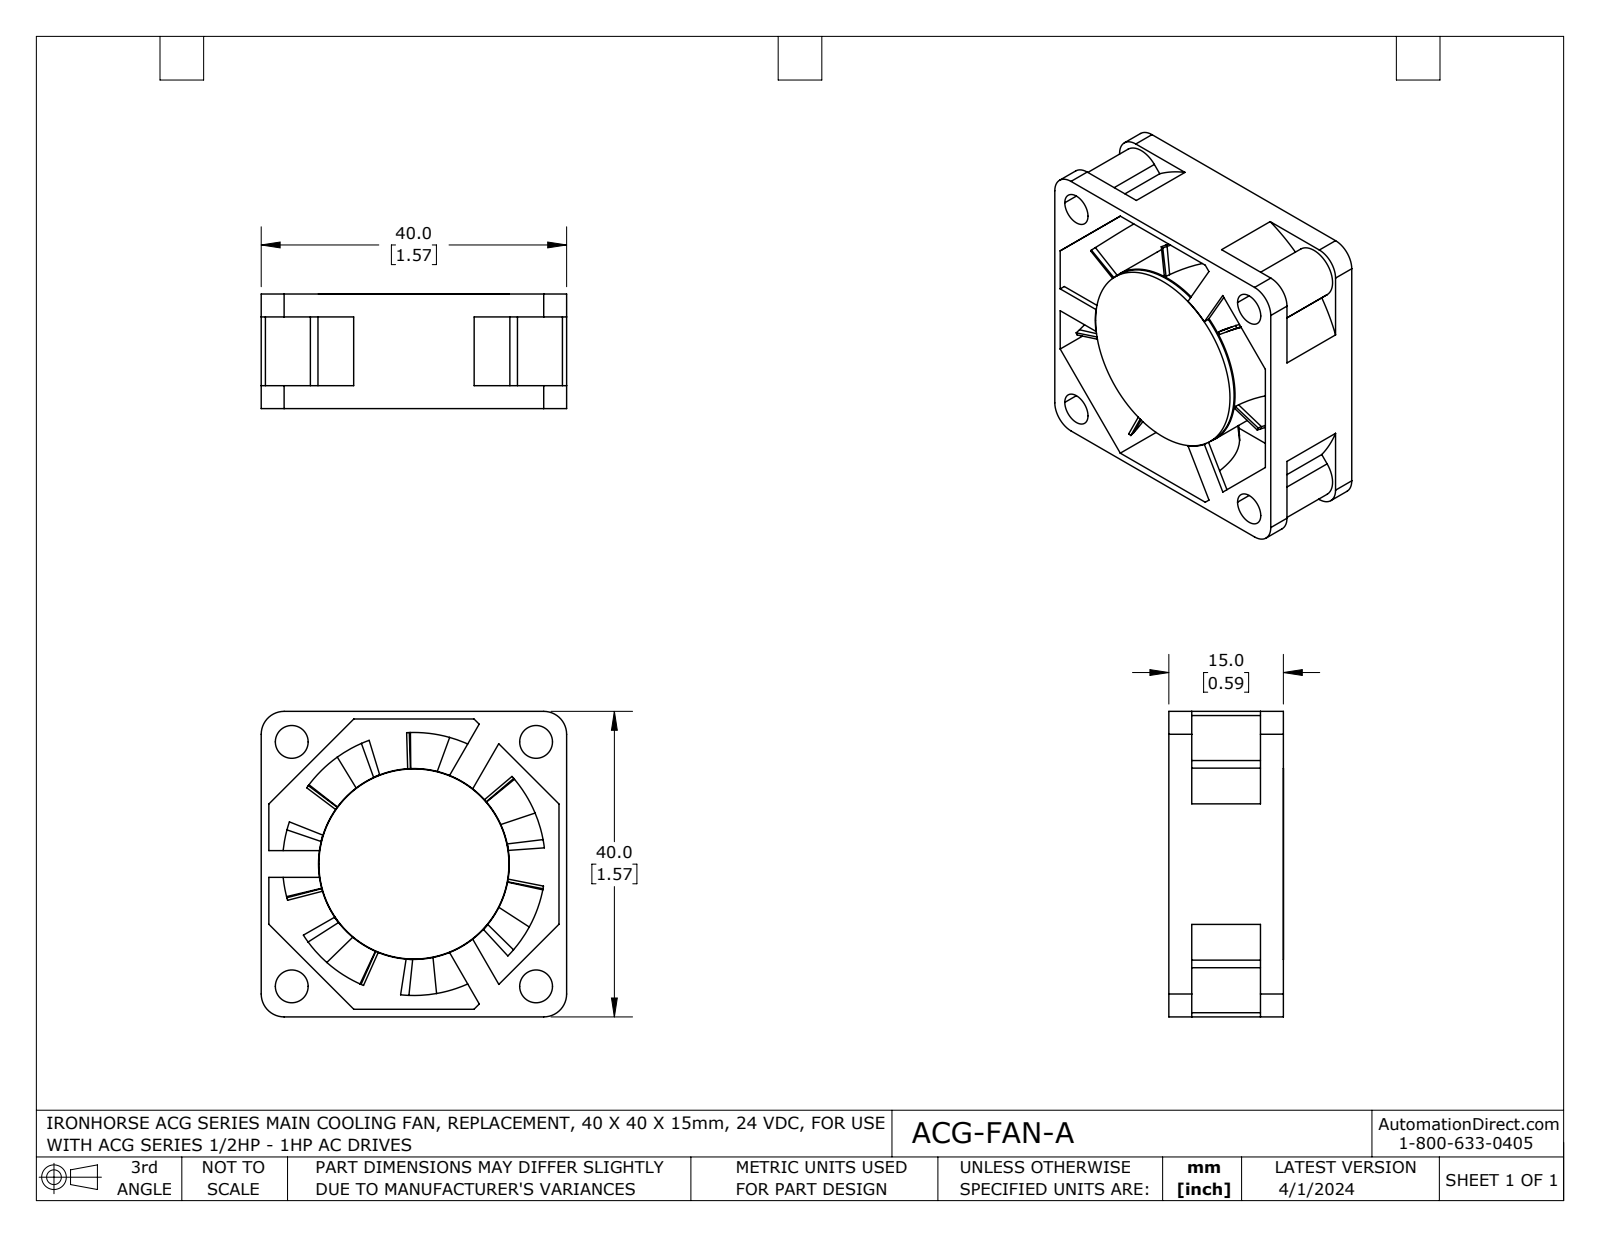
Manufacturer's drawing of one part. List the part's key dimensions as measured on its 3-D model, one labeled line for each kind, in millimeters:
Part name (STEP PRODUCT): ACG-FAN-A
STEP written by: SolidWorks 2021 (AUTOMOTIVE_DESIGN)
Units: millimetres
Bodies: 1 solid, 171 faces (52 planar, 49 cylindrical, 70 other)
Overall size (bounding box): 40 × 40 × 15
Volume: 6 690 mm³ · Surface area: 11 250 mm²
Round holes (diameter × count): ⌀4.3 ×4, ⌀23.6 ×1, ⌀25 ×1
Round bosses / shafts (diameter × count): ⌀24.9 ×1
Partial cylindrical surfaces — rounded edges, fillets, slot ends (radius × count): R3 ×4, R3.5 ×4, R17.2 ×1, R21.5 ×1
Main face-to-face distances: 1, 39, 38, 40, 15, 0.7, 12.5, 11.8, 14.3, 2.5
Hole centre spacings: 32, 22.6, 22.6, 45.2
